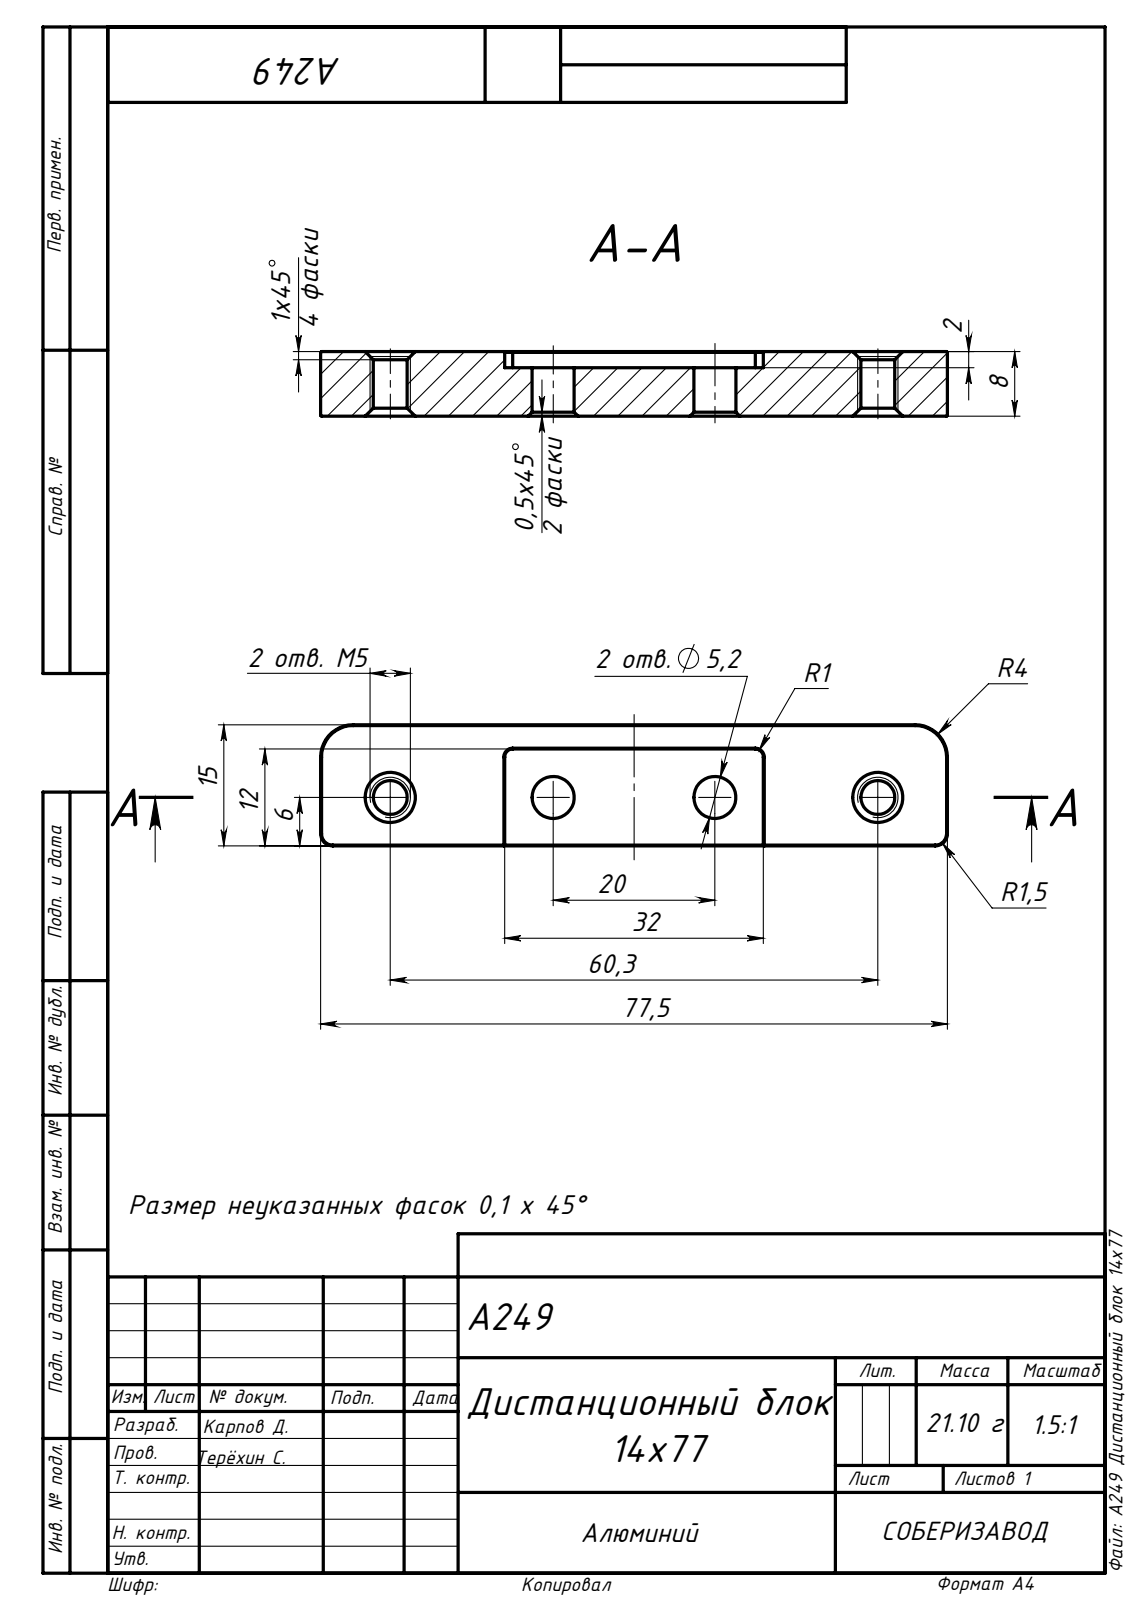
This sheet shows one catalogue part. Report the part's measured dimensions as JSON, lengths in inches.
{"part_name": "A249 Дистанционный блок 14х77", "step_written_by": "SolidWorks 2018 (AUTOMOTIVE_DESIGN)", "units": "inches", "bodies": {"solids": 1, "faces": 63, "planar": 27, "cylindrical": 14, "other": 22}, "overall_size": [3.051, 0.591, 0.315], "volume_in3": 0.486, "surface_area_in2": 6.208, "round_holes": [[0.165, 2], [0.205, 2]], "partial_cylinders_radius": [[0.039, 2], [0.059, 2], [0.157, 2]], "face_to_face_distances": [0.315, 0.591, 0.079, 0.236, 3.051, 0.472, 0.118, 0.896, 2.156, 1.26], "hole_center_spacings": [0.793, 1.581, 0.787, 2.374]}
